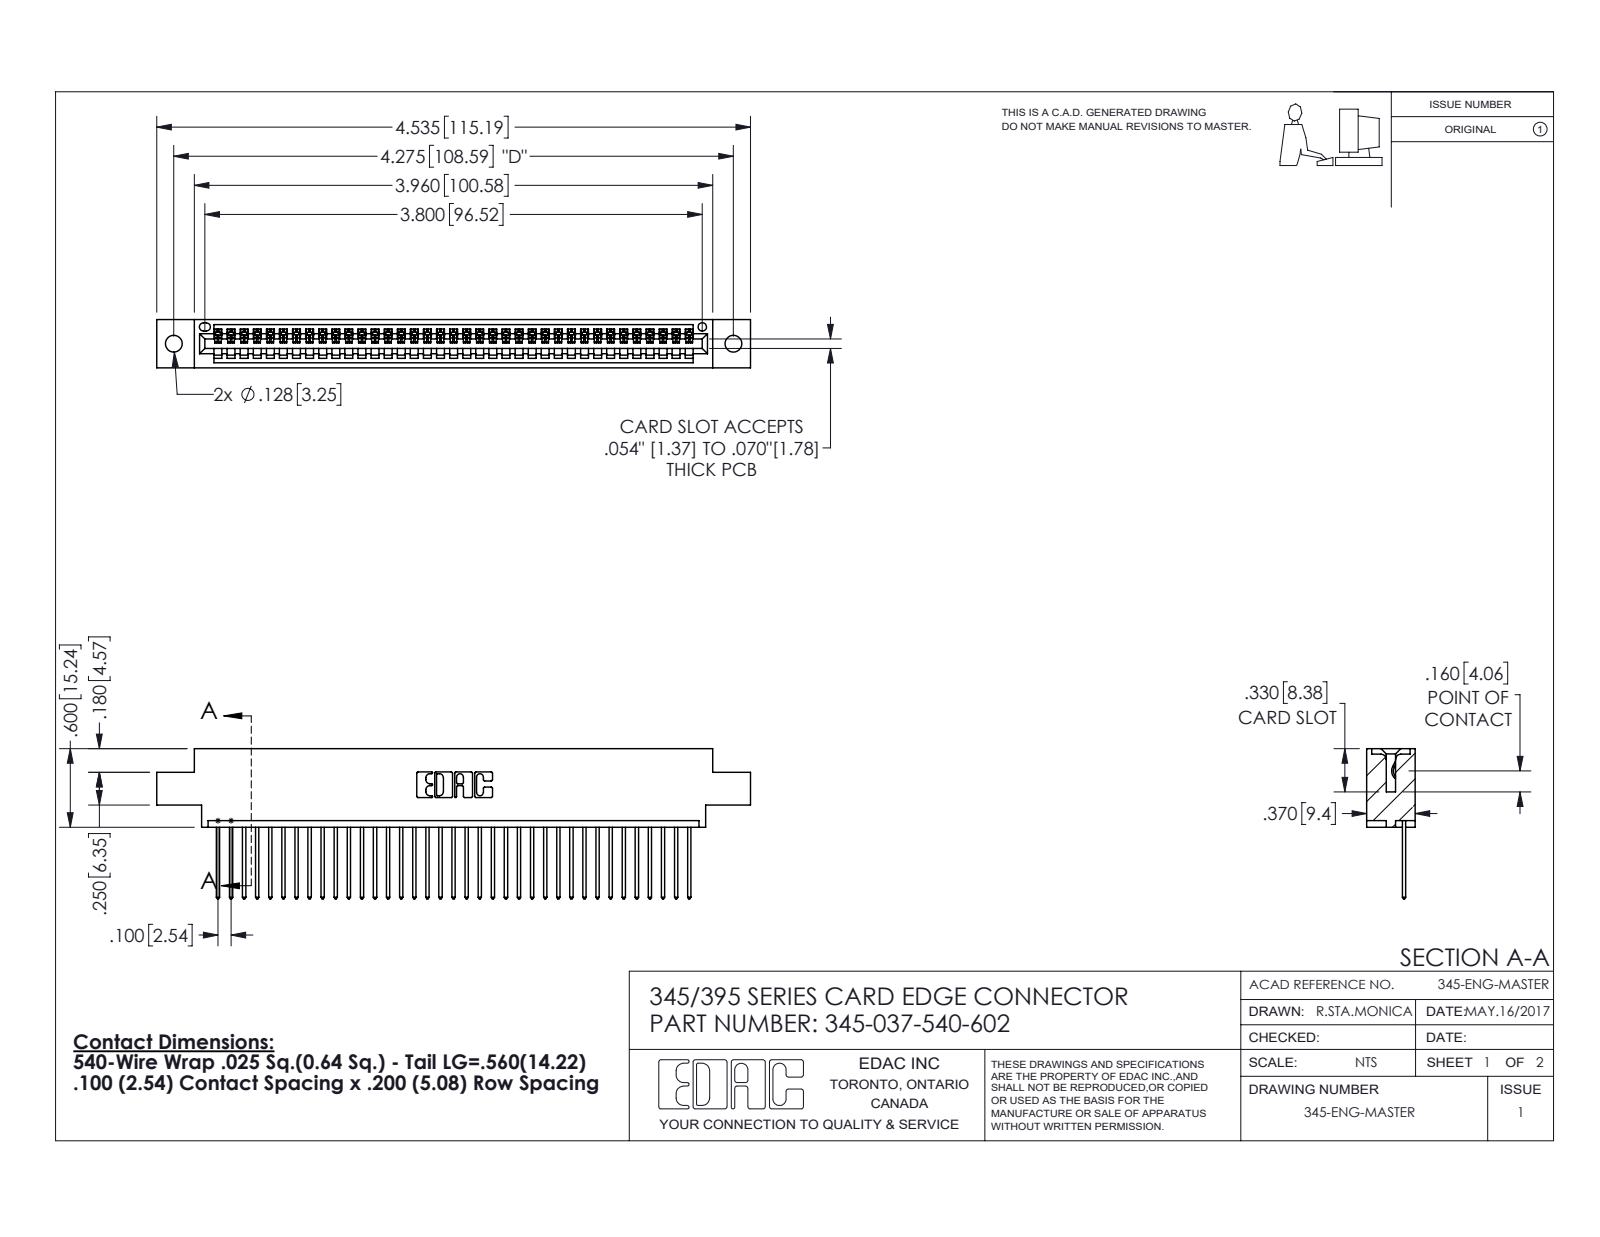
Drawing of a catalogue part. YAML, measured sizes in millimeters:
part_name: "345-037-540-602; 345 Part_0.170 Offset - 0.128 Dia; 345-292-001_345-293-140"
step_written_by: "SolidWorks 2016 (CONFIG_CONTROL_DESIGN)"
units: millimeters
bodies: {solids: 38, faces: 2276, planar: 1564, cylindrical: 712, other: 0}
overall_size: [115.2, 29.1, 9.4]
volume: 10800
surface_area: 14500
round_holes:
  - {diameter: 3.3, count: 2}
  - {diameter: 1.6, count: 1}
partial_cylinders:
  - {radius: 0.2, count: 74}
  - {radius: 0.3, count: 74}
  - {radius: 0.3, count: 22}
  - {radius: 0.2, count: 6}
  - {radius: 0.8, count: 6}
  - {radius: 0.7, count: 3}
  - {radius: 0.8, count: 2}
  - {radius: 1, count: 2}
face_to_face_distances: [7.6, 1.8, 9.4, 2.5, 6.9, 0.6, 5.1, 5.7, 4.4, 3.8]
hole_center_spacings: [6.9, 102.6, 108.6]
